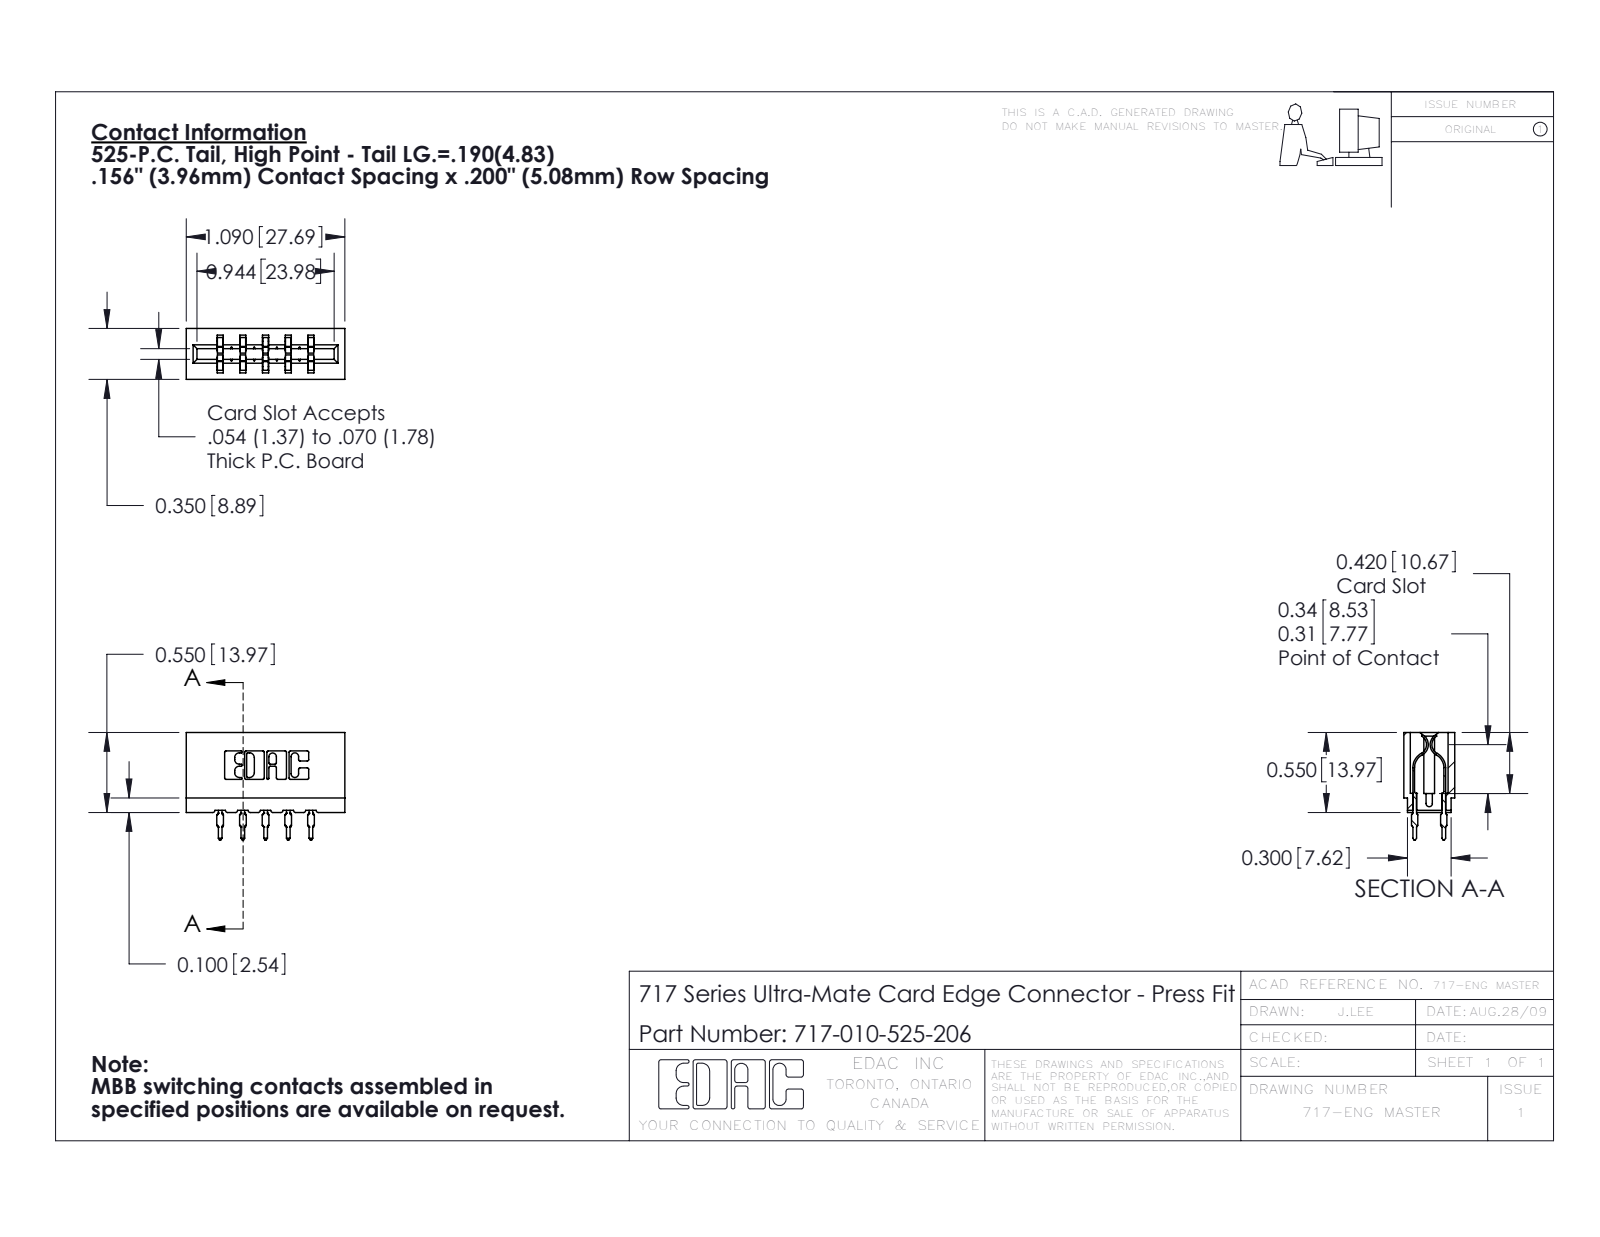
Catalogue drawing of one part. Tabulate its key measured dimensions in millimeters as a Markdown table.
| quantity | value |
| --- | --- |
| part name | 745-292-001_525; 717-010-525-206; 717 Part_Insulator Option - 06 |
| STEP written by | SolidWorks 2016 (CONFIG_CONTROL_DESIGN) |
| units | millimeters |
| bodies | 11 solids, 994 faces (519 planar, 215 cylindrical, 260 other) |
| overall size | 27.7 × 18.8 × 8.9 |
| volume | 2 560 mm³ |
| surface area | 3 392 mm² |
| partial cylindrical surfaces (radius × count) | 0.3 × 22, 0.5 × 20, 0.4 × 10, 0.1 × 8, 0.3 × 8, 0.2 × 6, 0.8 × 6, 0.7 × 3 |
| main face-to-face distances | 5.4, 4, 3.5, 8.9, 5, 1.1, 7.9, 7.9, 11.9, 1.9 |
